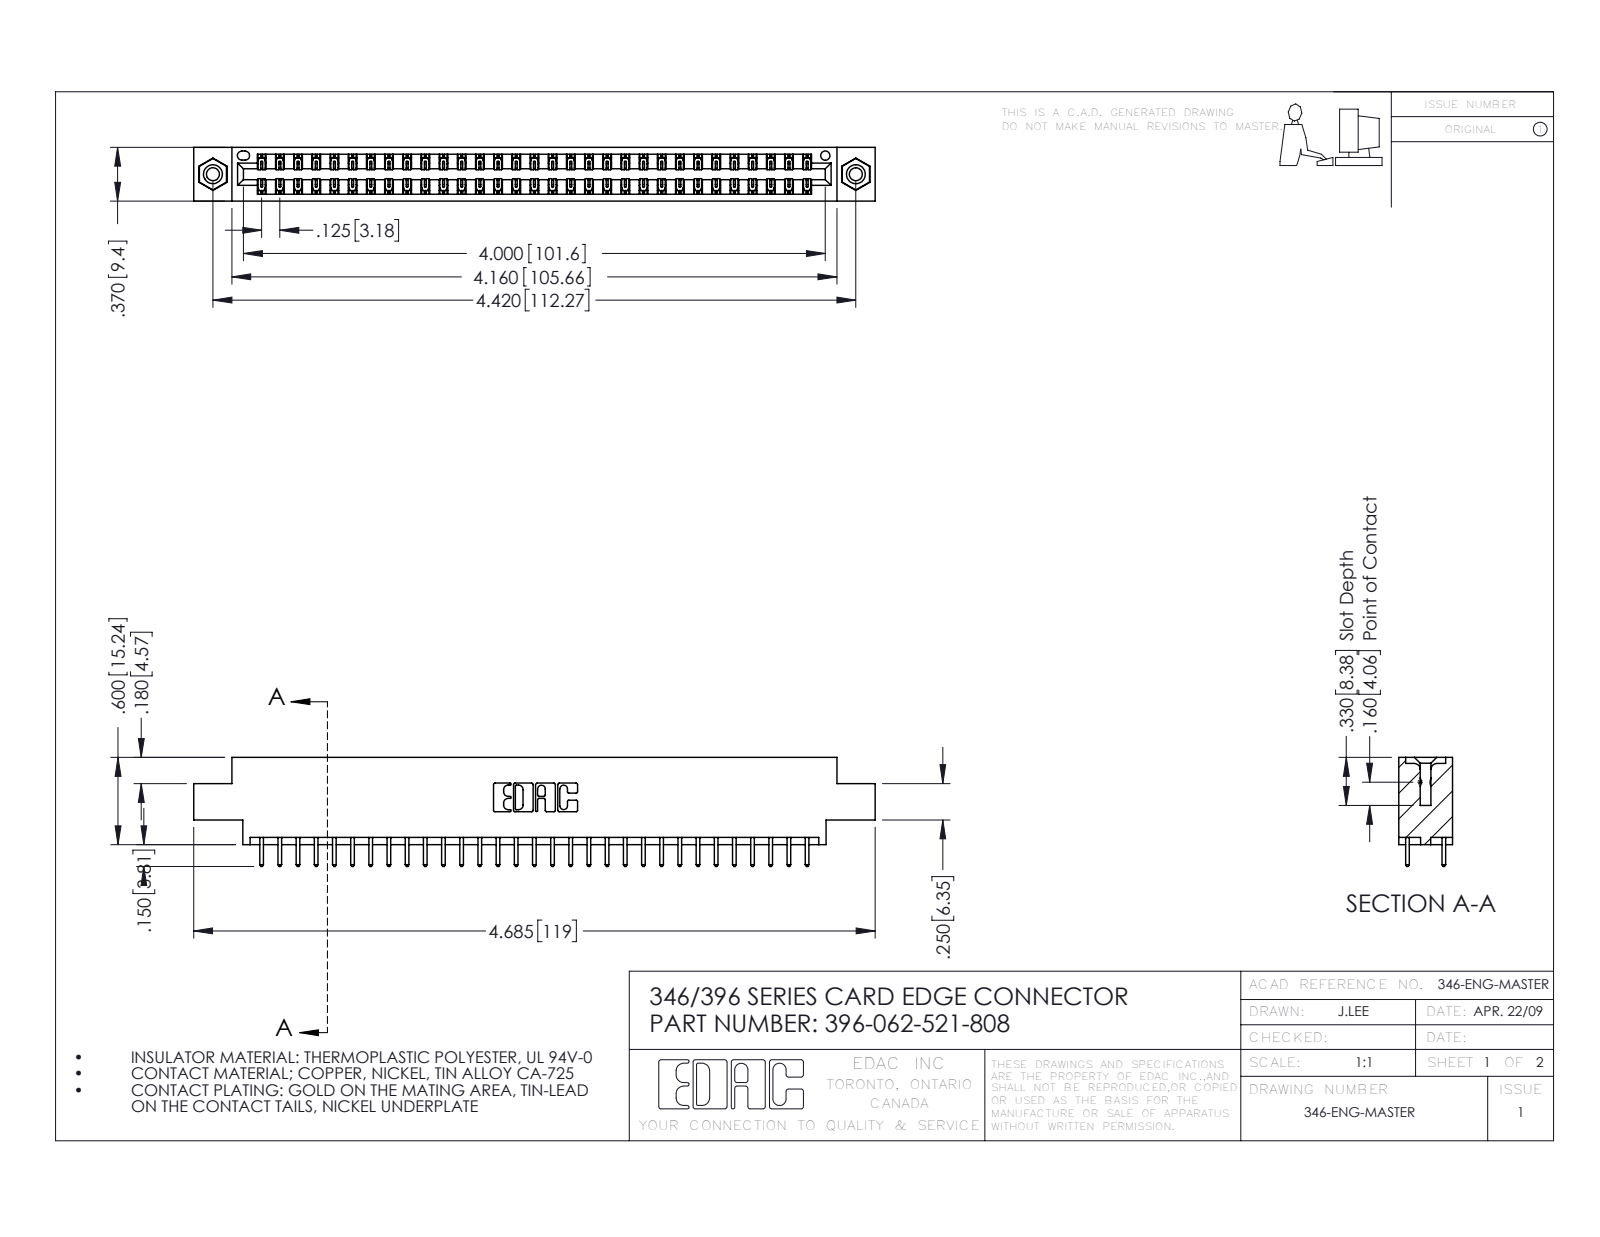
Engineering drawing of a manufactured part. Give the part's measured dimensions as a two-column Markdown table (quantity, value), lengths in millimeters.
| quantity | value |
| --- | --- |
| part name | 345-250-001_345-250-003-102; 345-292-001_345-293-121; 346 Part_0.170 Offset - 0.156 Dia-TI; 396-062-521-808 |
| STEP written by | SolidWorks 2016 (CONFIG_CONTROL_DESIGN) |
| units | millimeters |
| bodies | 65 solids, 3410 faces (2282 planar, 1112 cylindrical, 16 other) |
| overall size | 119 × 19.1 × 9.4 |
| volume | 11 300 mm³ |
| surface area | 15 430 mm² |
| round holes (diameter × count) | 2.3 × 2, 3.2 × 2, 4 × 2, 1.6 × 1 |
| round bosses / shafts (diameter × count) | 3.9 × 2 |
| partial cylindrical surfaces (radius × count) | 0.2 × 93, 0.3 × 62, 0.3 × 22, 0.2 × 6, 0.8 × 6, 0.7 × 3, 0.4 × 2, 0.6 × 2 |
| main face-to-face distances | 1.2, 8.2, 9.4, 6.4, 1.8, 7.6, 0.6, 7, 5.6, 3.8 |
| hole center spacings | 6.2, 107, 112.3 |
